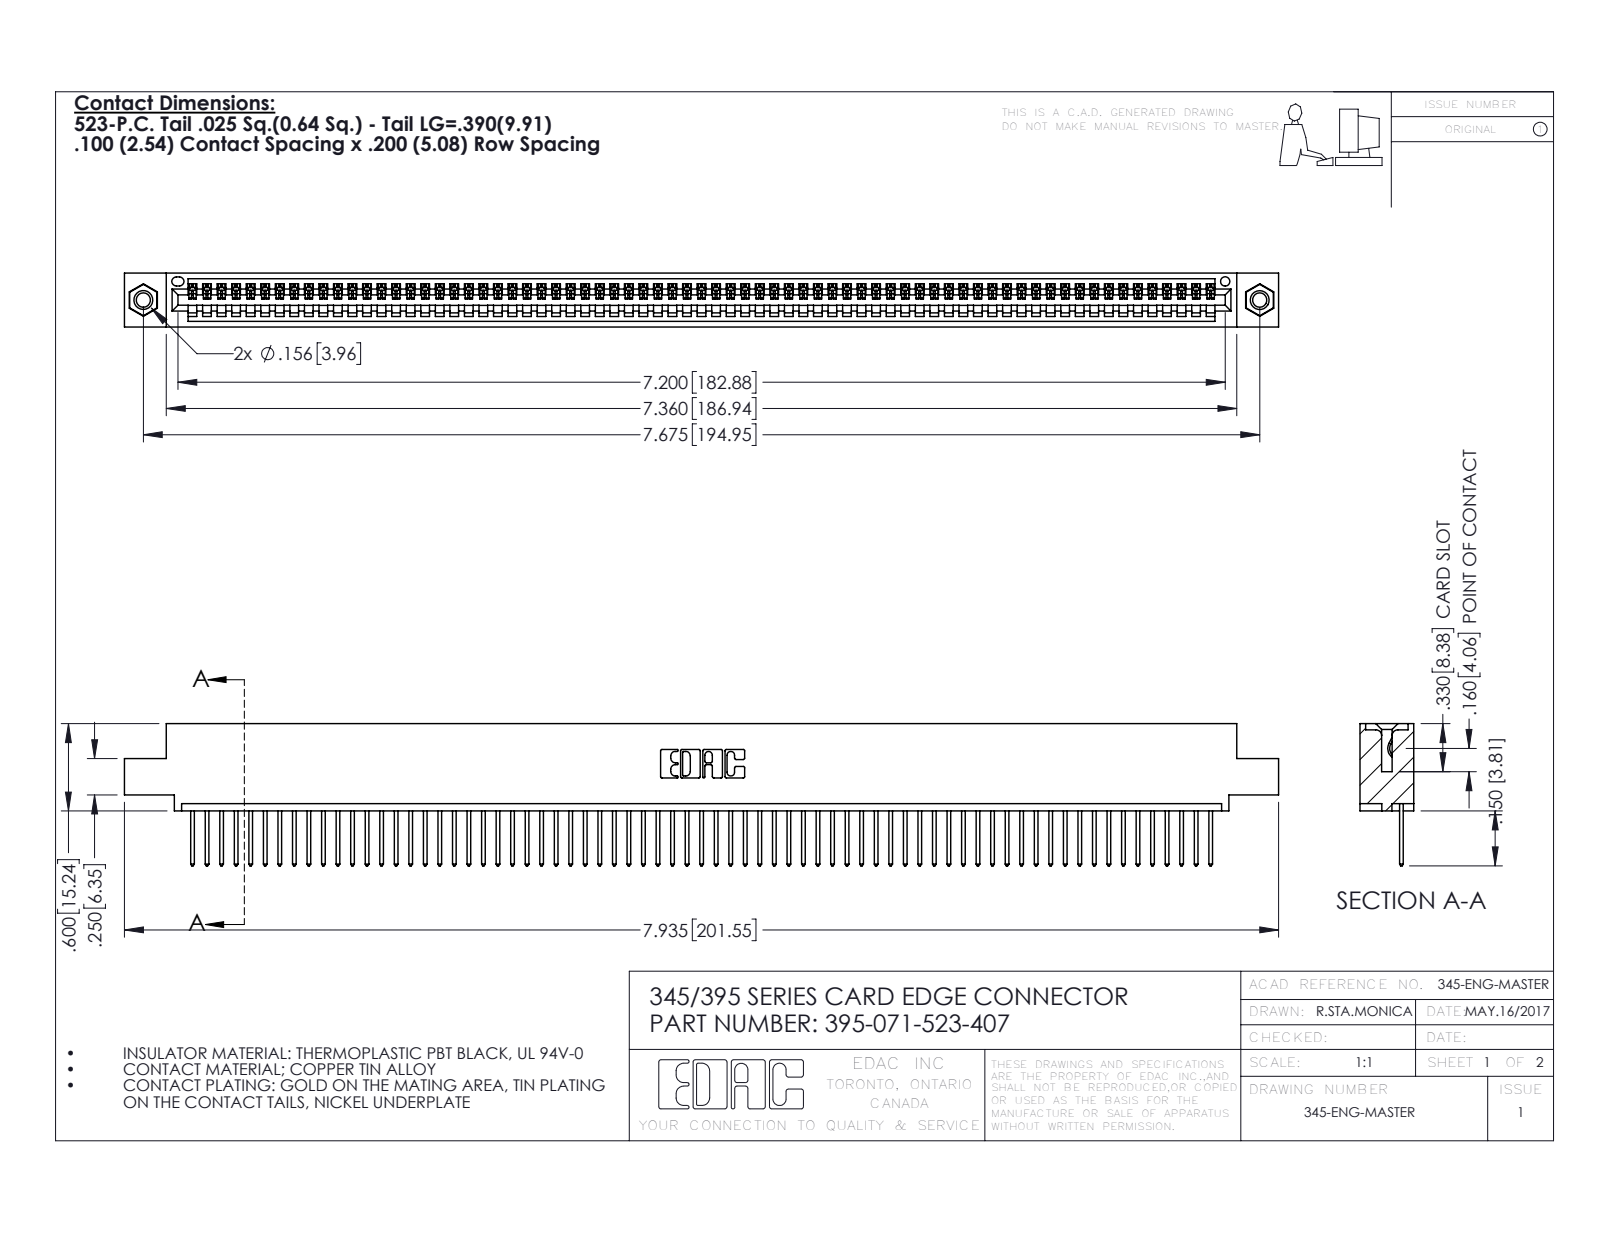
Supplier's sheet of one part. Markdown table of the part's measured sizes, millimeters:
| quantity | value |
| --- | --- |
| part name | 395-071-523-407; 345 Part_0.110 Offset - 0.156 Dia-TI; 345-292-001_345-293-123; 345-250-001_345-250-005-103 |
| STEP written by | SolidWorks 2016 (CONFIG_CONTROL_DESIGN) |
| units | millimeters |
| bodies | 74 solids, 4308 faces (2956 planar, 1336 cylindrical, 16 other) |
| overall size | 201.5 × 24.8 × 9.4 |
| volume | 19 270 mm³ |
| surface area | 26 190 mm² |
| round holes (diameter × count) | 2.5 × 2, 3.2 × 2, 4 × 2, 1.6 × 1 |
| round bosses / shafts (diameter × count) | 3.9 × 2 |
| partial cylindrical surfaces (radius × count) | 0.2 × 142, 0.3 × 142, 0.3 × 22, 0.2 × 6, 0.8 × 6, 0.7 × 3, 0.8 × 2, 1 × 2 |
| main face-to-face distances | 1.8, 7.6, 9.4, 5.1, 2.5, 6.9, 0.6, 5.7, 3.8, 1.8 |
| hole center spacings | 6.9, 189, 194.9 |
